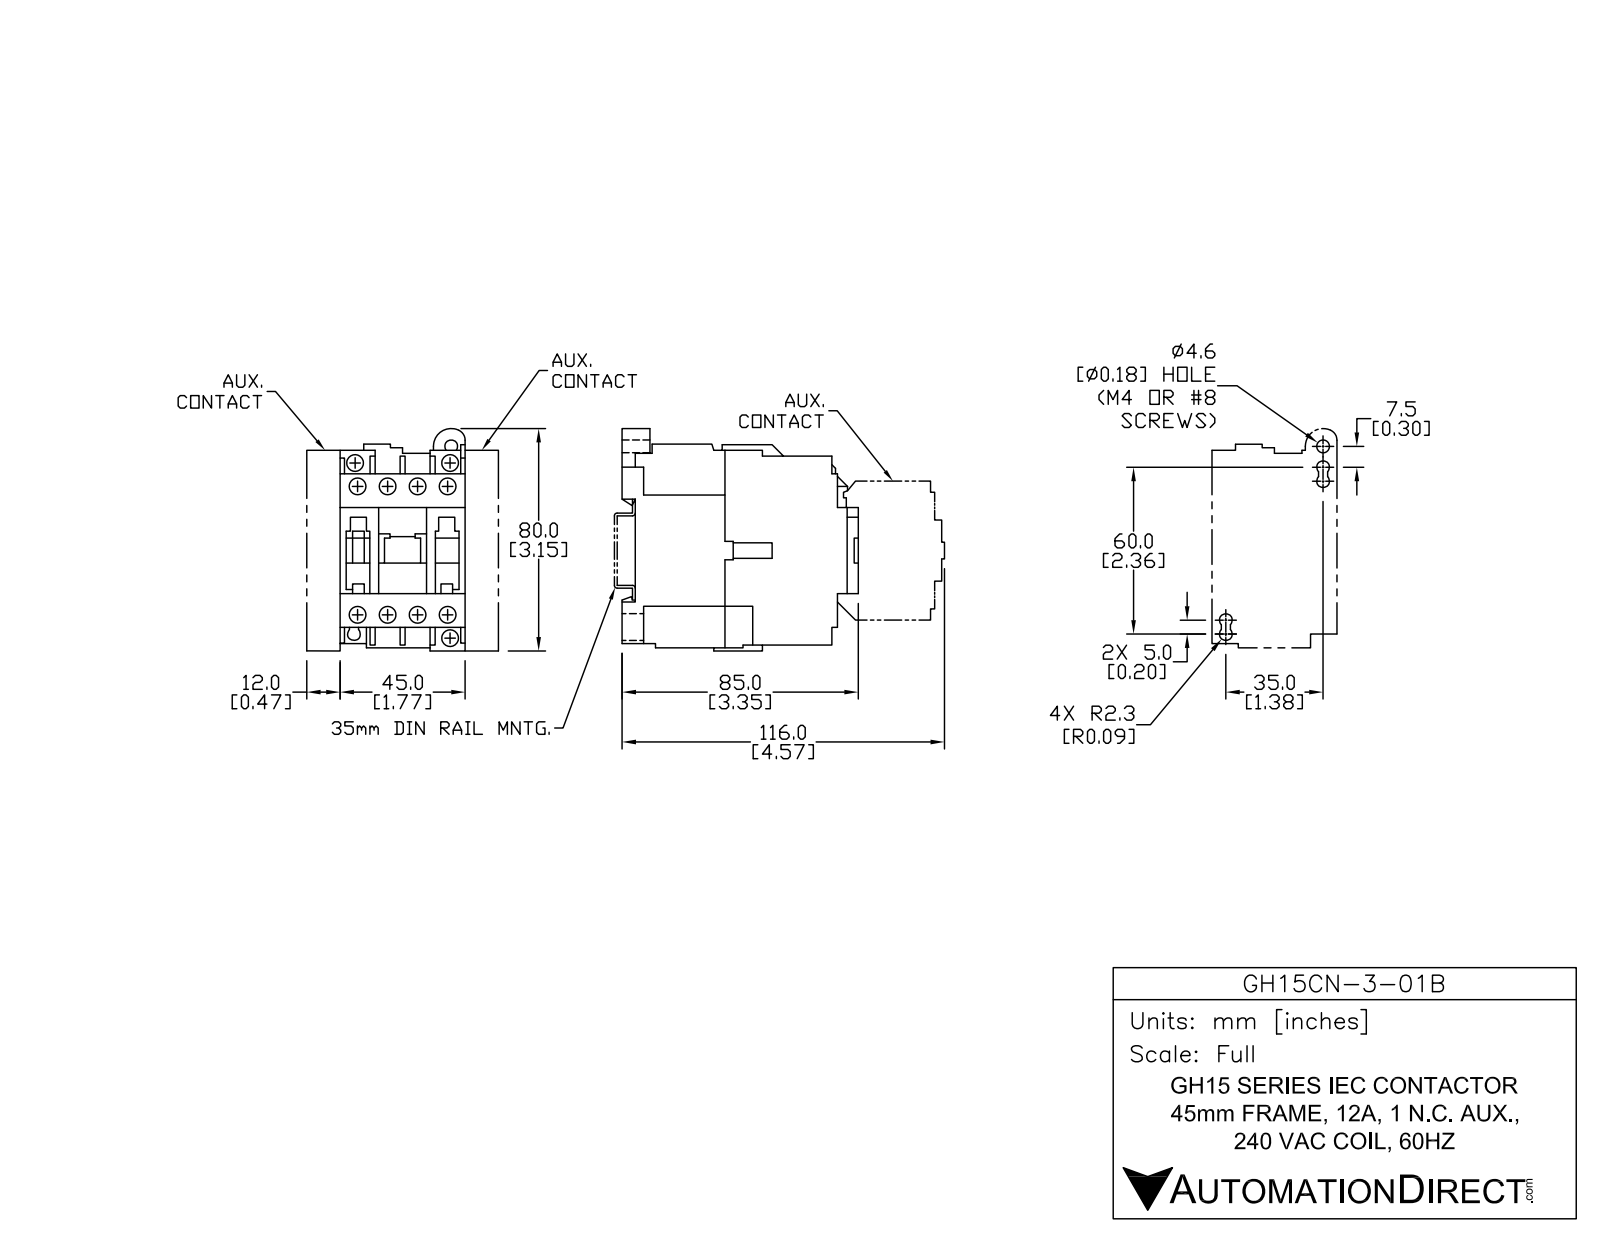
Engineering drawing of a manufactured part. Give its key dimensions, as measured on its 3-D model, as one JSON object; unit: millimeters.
{"part_name": "GH15CN-3-01B", "step_written_by": "SolidWorks 2009 (AUTOMOTIVE_DESIGN)", "units": "millimeters", "bodies": {"solids": 1, "faces": 661, "planar": 442, "cylindrical": 65, "other": 154}, "overall_size": [85.5, 80, 45], "volume_mm3": 196351, "surface_area_mm2": 35792, "round_holes": [[6.25, 9], [6.5, 2], [4.6, 1]], "partial_cylinders_radius": [[1, 10], [2.3, 8], [4.75, 8], [3, 2], [4.99, 1], [5, 1]], "face_to_face_distances": [45, 9.5, 35.5, 12.12, 23.38, 8, 7, 33.75, 10.38, 32.87], "hole_center_spacings": [11.25, 47.12, 22.5, 45.76, 50.99, 7.62, 33.75, 53.38]}
